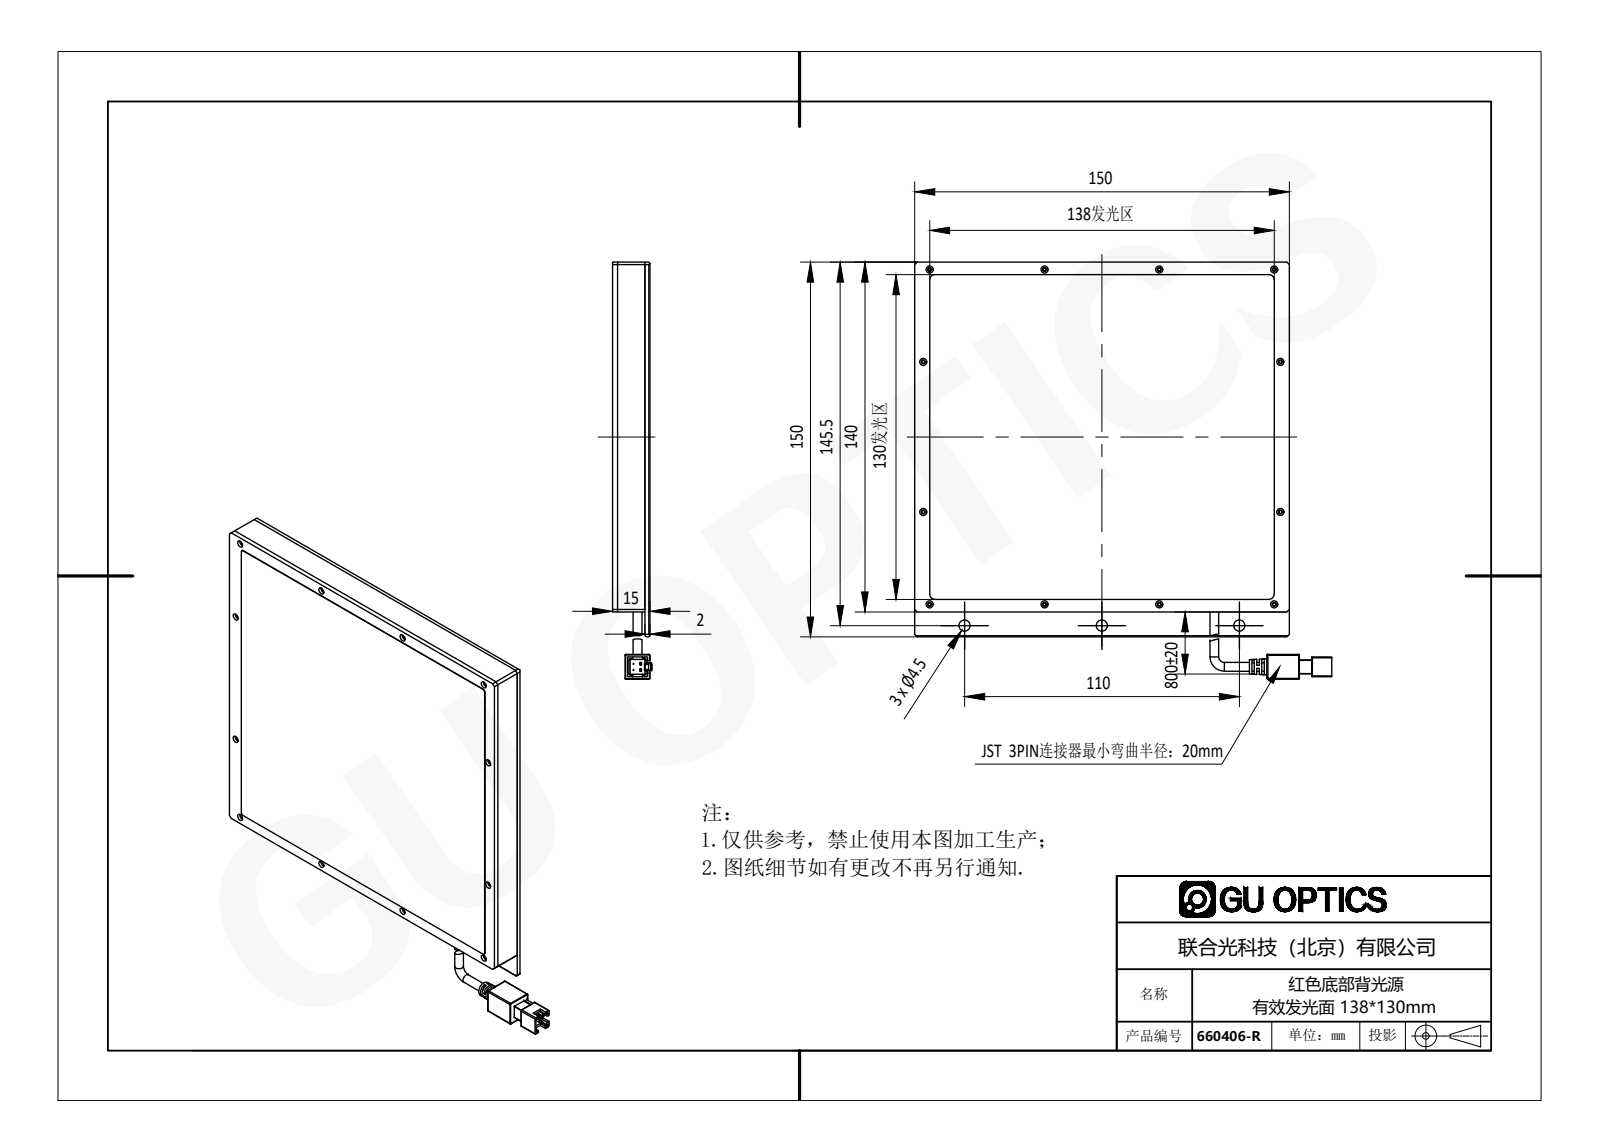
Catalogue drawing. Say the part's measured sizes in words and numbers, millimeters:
The part is named "660406-R". Its 3-D file was written by "SolidWorks 2016 (AUTOMOTIVE_DESIGN)". It is 22 solids with 3021 faces: 2610 planar, 253 cylindrical and 158 other. Overall it measures 167 by 167 by 15.9 millimeters. Its volume is 165 313 cubic millimeters and its surface area 154 286 square millimeters. Round holes: 12 of diameter 1.1, 12 of diameter 1.4, 12 of diameter 1.5, 12 of diameter 1.6, 12 of diameter 2, 12 of diameter 2.2, 12 of diameter 2.8, 3 of diameter 4.5. Round bosses or shafts: 2 of diameter 3.5. Partial cylindrical surfaces (rounded edges, fillets, slot ends): 15 of radius 0.1, 13 of radius 0.2, 12 of radius 0.4, 6 of radius 1, 4 of radius 2, 2 of radius 1.5, 1 of radius 0.3, 1 of radius 0.68. The main face-to-face distances are 2, 11, 13, 15.2, 13.2, 2.2, 4, 9, 11.2, 5. The hole center spacings are 46, 141.68, 37.08, 61, 92, 97.03, 101.49, 108.45.
